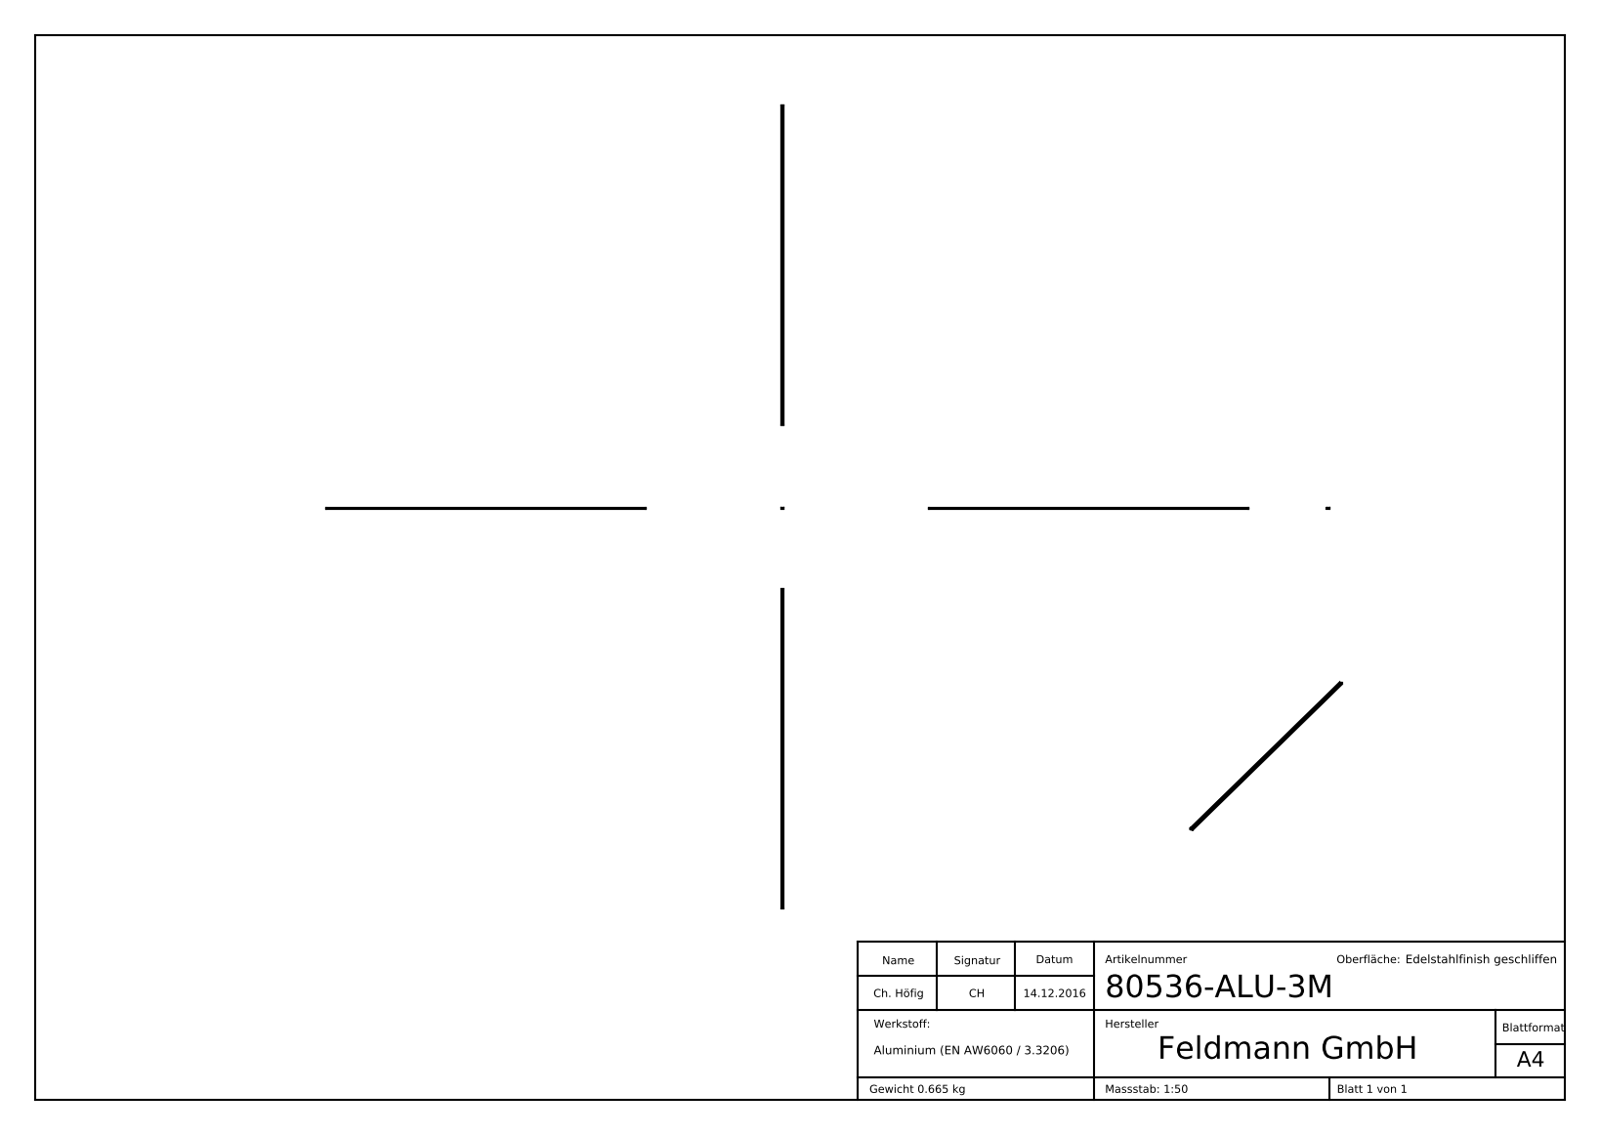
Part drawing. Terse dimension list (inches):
name: 80536-ALU-3M
written by: SolidWorks 2015 (CONFIG_CONTROL_DESIGN)
unit: in
bodies: 1 solid, 304 faces (172 planar, 6 cylindrical, 126 other)
size: 118.11 × 0.866 × 0.472
volume: 15.02 in³; area: 397.5 in²
rounds: 4× R0.02, 2× R0.079
face distances: 0.079, 0.787, 0.866, 0.709, 0.394, 0.472, 118.11, 0.075, 0.713, 0.791
